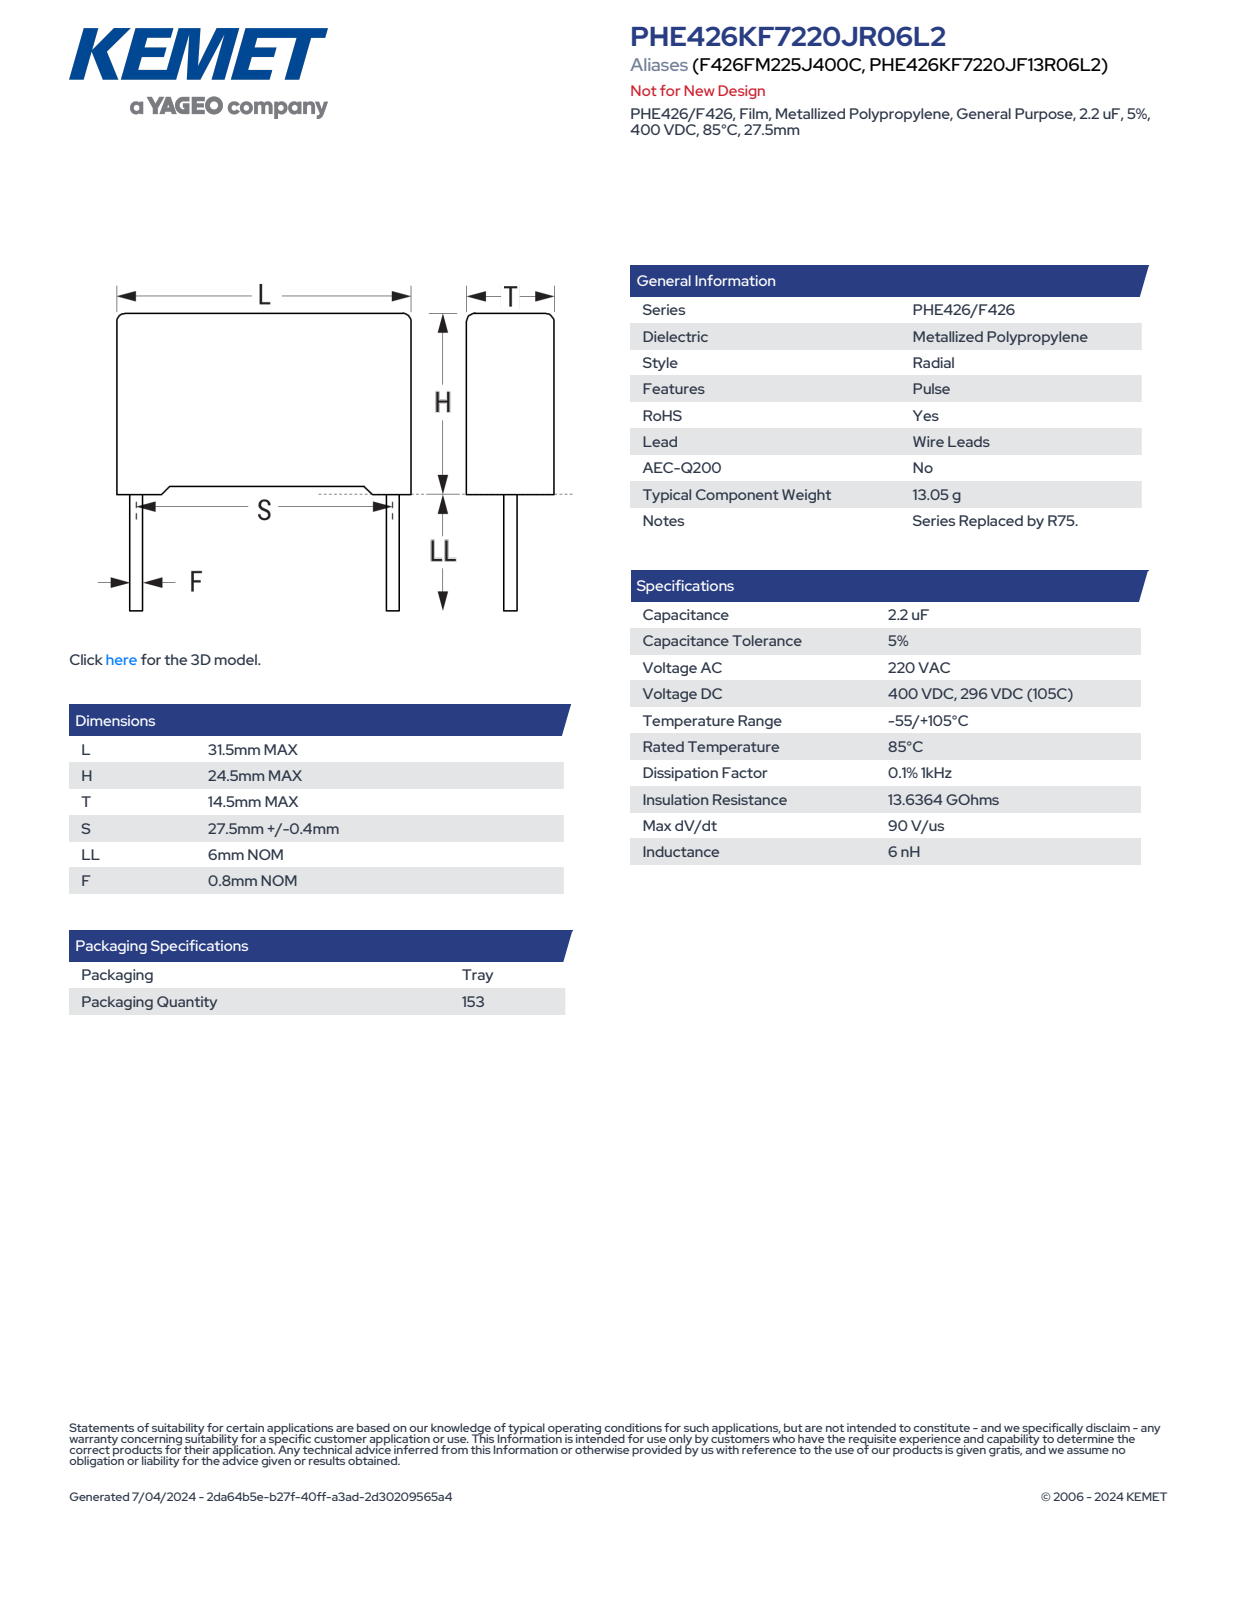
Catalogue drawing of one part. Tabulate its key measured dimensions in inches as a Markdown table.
| quantity | value |
| --- | --- |
| part name | CFR_RB2_31.5X24.5X14.5_L31.5H24.5T14.5S27.5LL6F0.8 |
| STEP written by | SolidWorks 2021 (AUTOMOTIVE_DESIGN) |
| units | inches |
| bodies | 4 solids, 85 faces (77 planar, 8 cylindrical, 0 other) |
| overall size | 1.24 × 1.201 × 0.571 |
| volume | 0.662 in³ |
| surface area | 5.03 in² |
| round bosses / shafts (diameter × count) | 0.031 × 2 |
| partial cylindrical surfaces (radius × count) | 0.02 × 4 |
| main face-to-face distances | 0.571, 1.24, 0.931, 0.935, 0.03, 0.033, 0.965, 0.041, 1.199, 0.571 |
